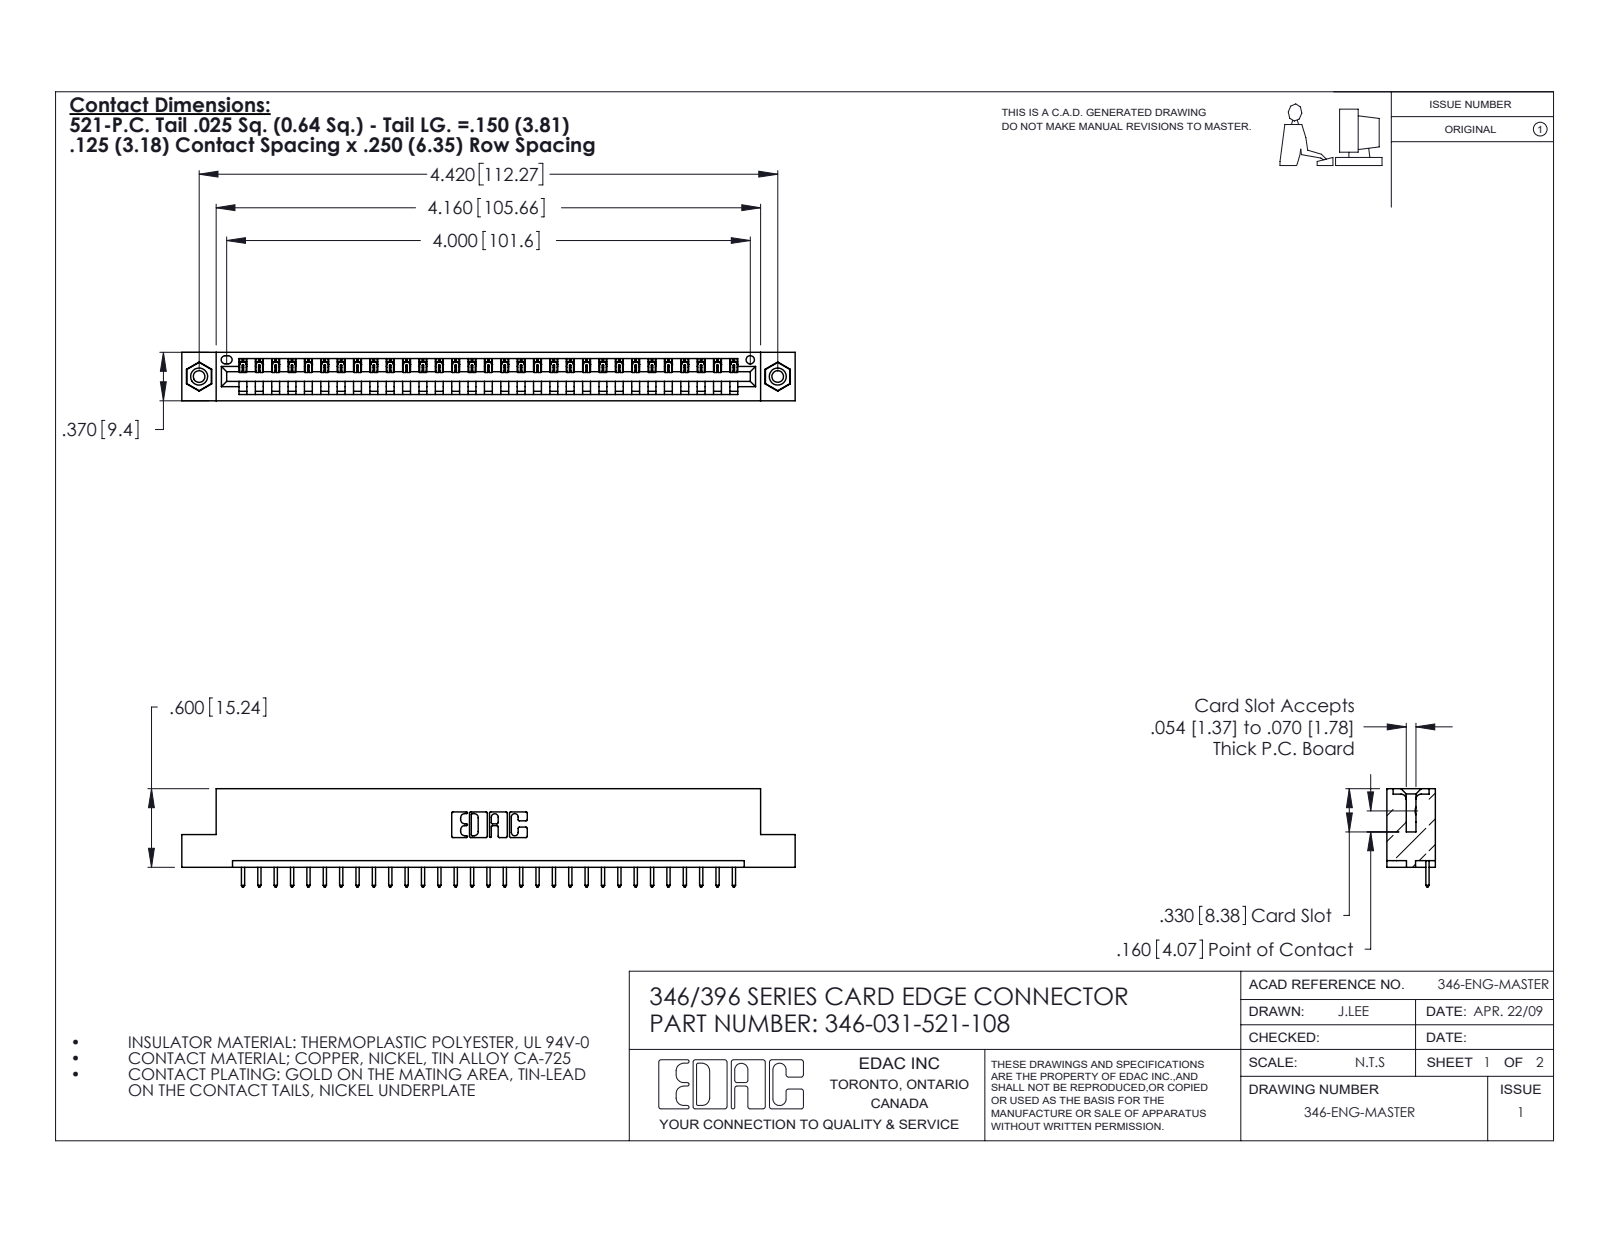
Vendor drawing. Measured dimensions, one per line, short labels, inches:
name: 345-292-001_345-293-121; 345-250-001_345-250-003-102; 346-031-521-108; 346 Part_Flush Mounting Lugs - 0.156 Dia-TI
written by: SolidWorks 2020 (CONFIG_CONTROL_DESIGN)
unit: in
bodies: 34 solids, 1980 faces (1348 planar, 616 cylindrical, 16 other)
size: 4.685 × 0.75 × 0.37
volume: 0.685 in³; area: 21.04 in²
holes: 2× ⌀0.089, 2× ⌀0.125, 2× ⌀0.156, 1× ⌀0.064
bosses: 2× ⌀0.155
rounds: 62× R0.006, 62× R0.01, 22× R0.01, 6× R0.007, 6× R0.031, 3× R0.026, 2× R0.031, 2× R0.04
face distances: 0.048, 0.322, 0.37, 0.25, 0.072, 0.298, 0.025, 0.148, 0.222, 0.1
hole spacings: 0.246, 4.212, 4.42
